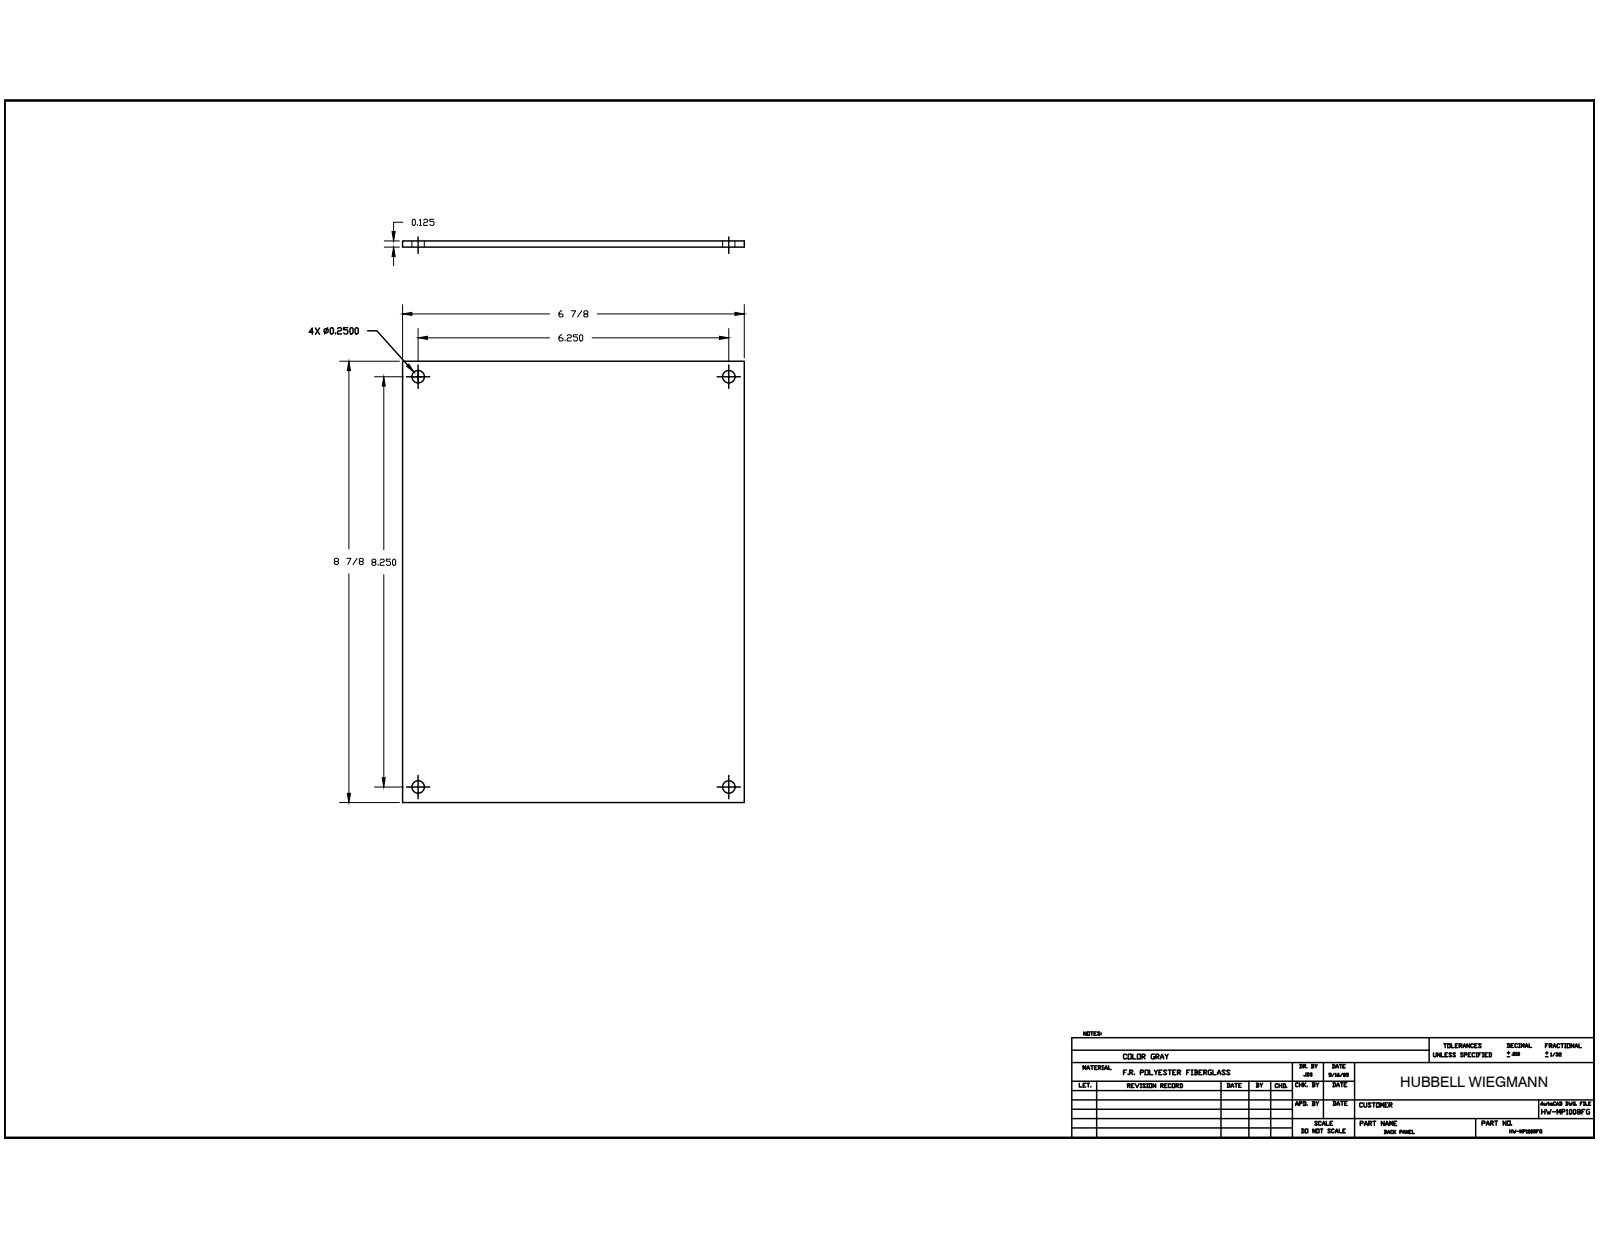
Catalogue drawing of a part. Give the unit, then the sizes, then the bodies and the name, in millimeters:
Units: millimetres
Overall size (bounding box): 225.43 × 174.62 × 3.17
Round holes (diameter × count): ⌀6.35 ×4
Main face-to-face distances: 3.17, 174.62, 225.42
Hole centre spacings: 158.76, 209.54, 262.89
Volume: 124 581 mm³ · Surface area: 81 270 mm²
Bodies: 1 solid, 10 faces (6 planar, 4 cylindrical, 0 other)
Part name (STEP PRODUCT): BP108FG_STP
STEP written by: Autodesk Inventor 2014 (AUTOMOTIVE_DESIGN)
